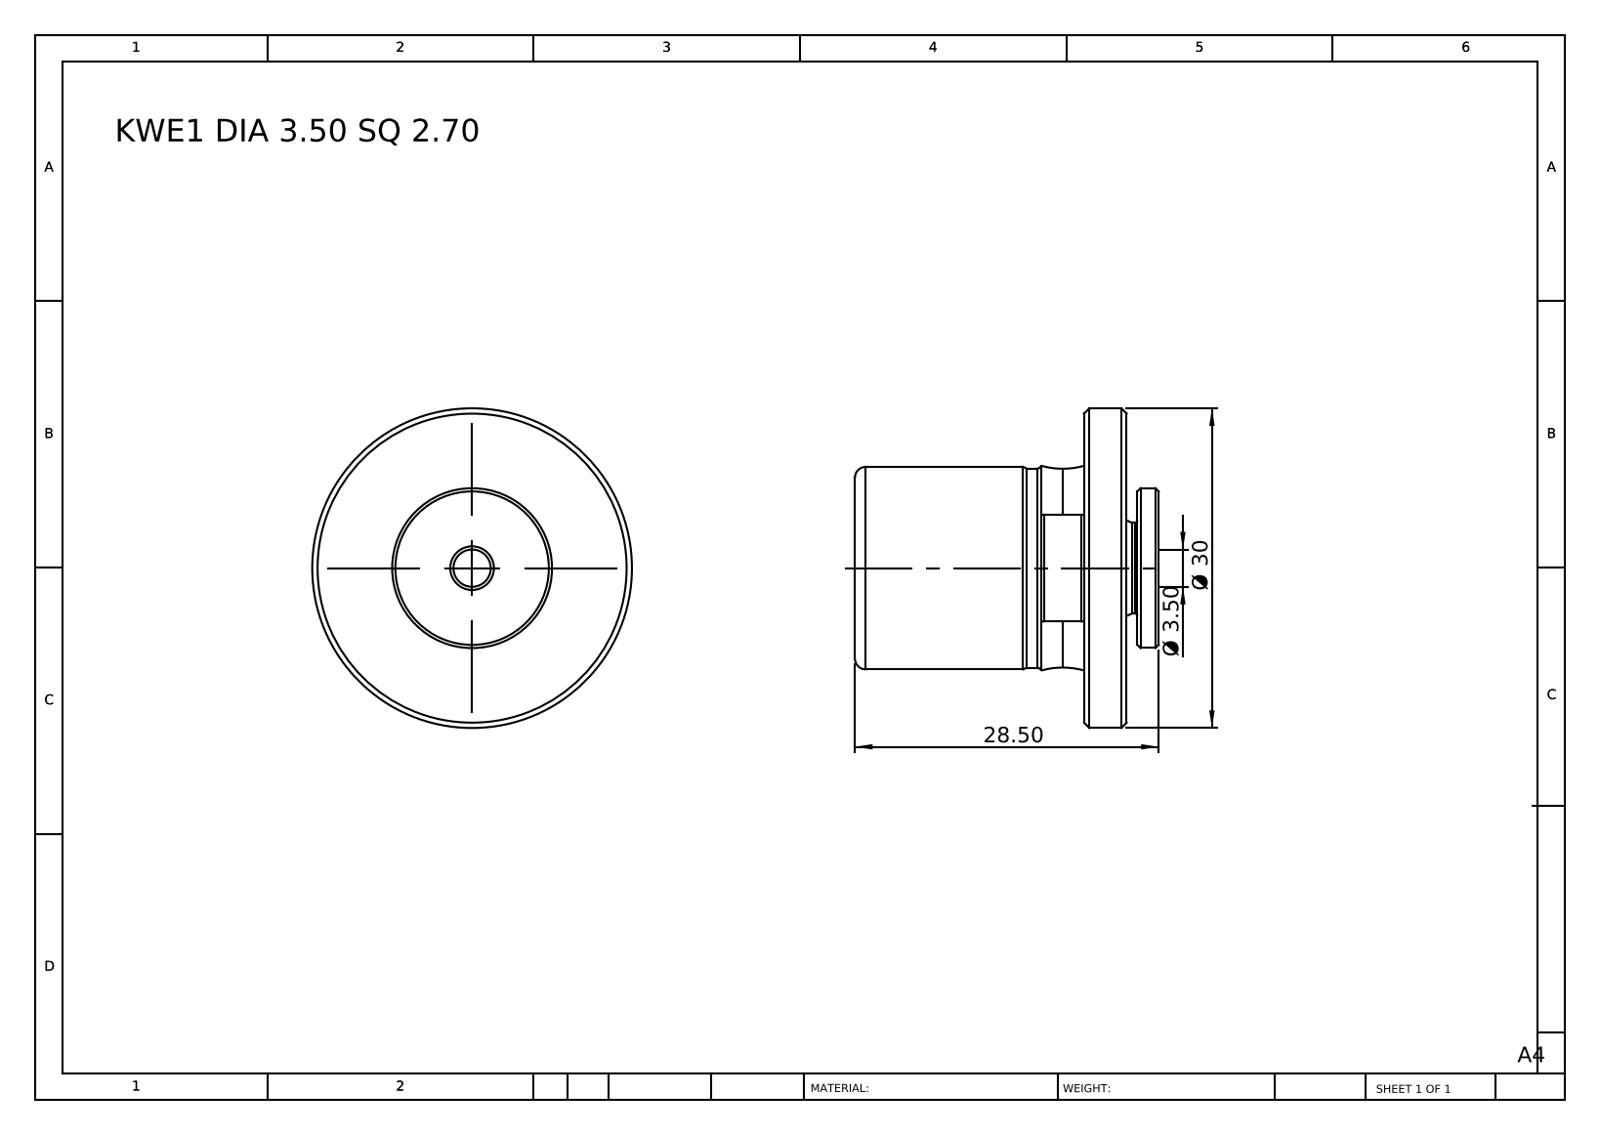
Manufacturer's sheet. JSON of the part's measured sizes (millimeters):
{"part_name": "KWE1 DIA 3.50 SQ 2.70", "step_written_by": "SolidWorks 2014 (CONFIG_CONTROL_DESIGN)", "units": "millimeters", "bodies": {"solids": 1, "faces": 56, "planar": 12, "cylindrical": 14, "other": 30}, "overall_size": [30, 30, 28.5], "volume_mm3": 9414, "surface_area_mm2": 3495, "round_holes": [[3.5, 1]], "round_bosses_or_shafts": [[30, 1], [19, 1], [18.7, 1], [15, 1], [8.5, 1]], "partial_cylinders_radius": [[12.4, 1]], "face_to_face_distances": [4, 21.5, 25.5, 3, 7, 28.5, 1, 26.5, 5, 2]}
